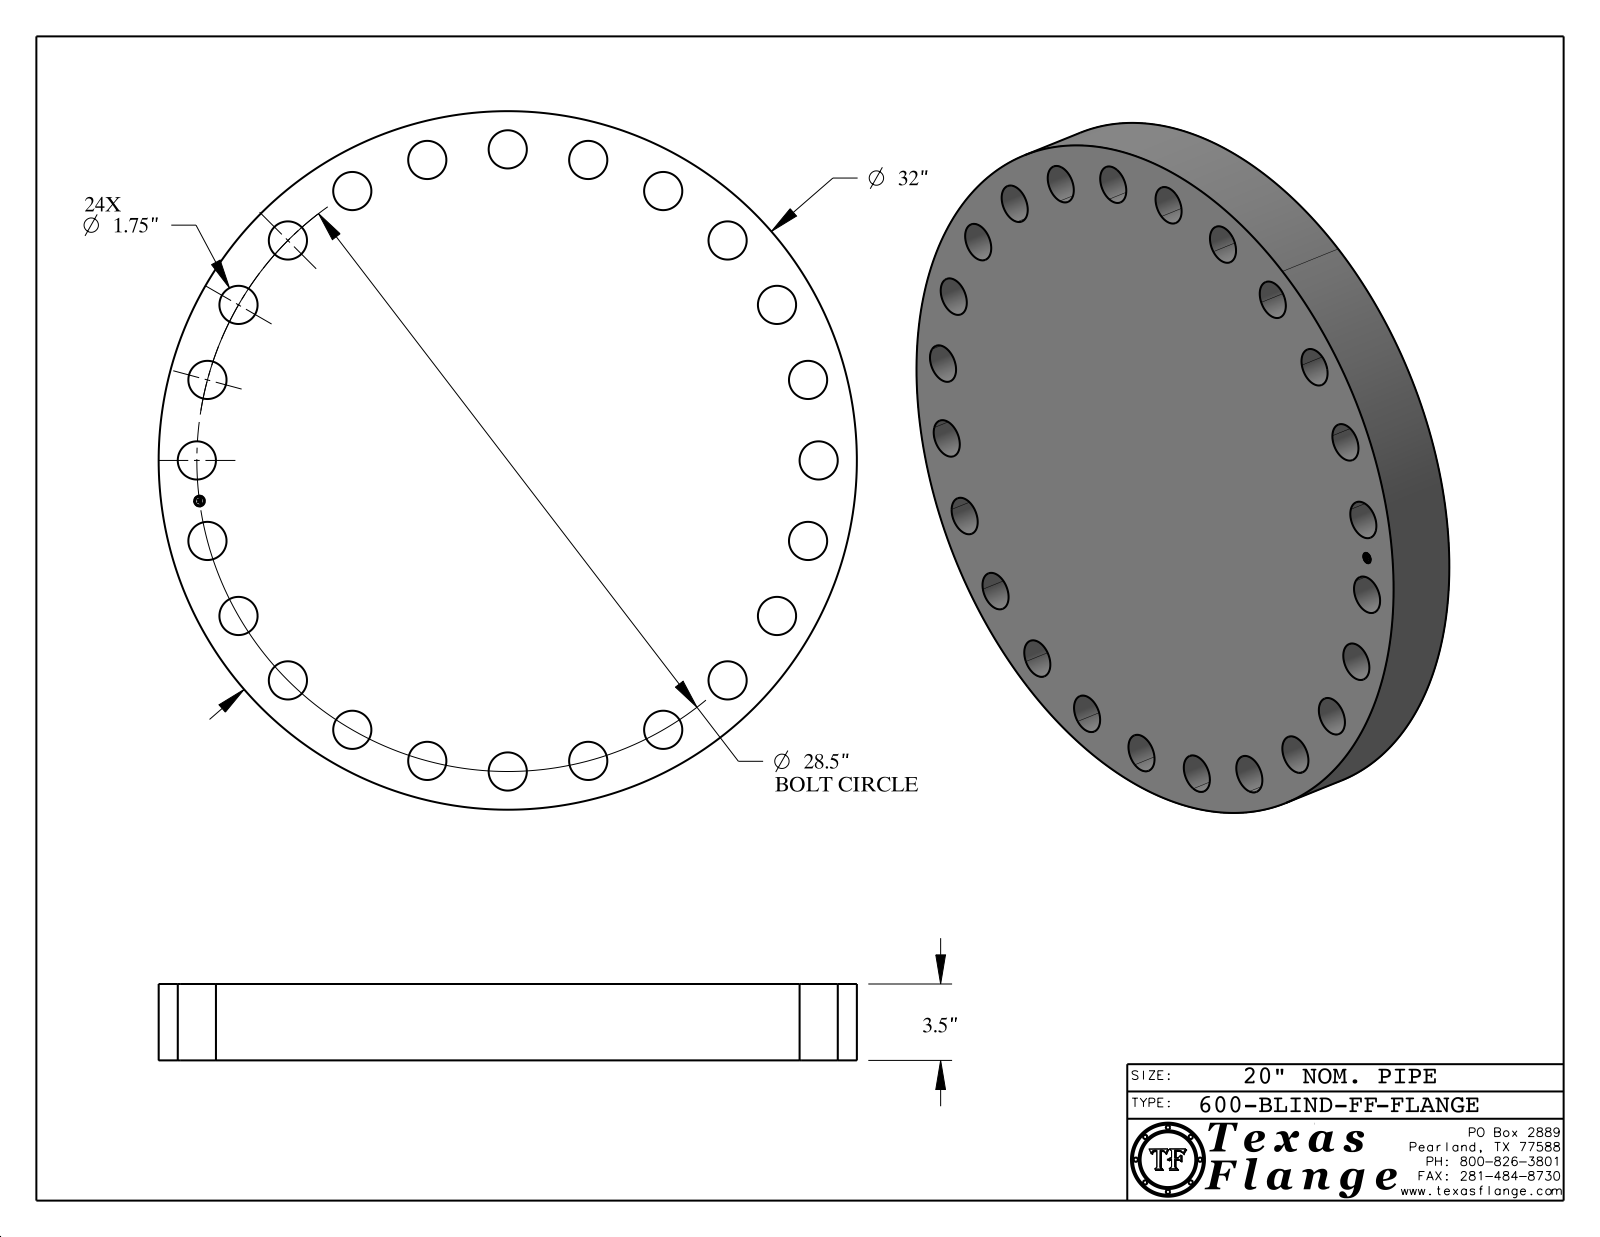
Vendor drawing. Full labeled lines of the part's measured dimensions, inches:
Part name (STEP PRODUCT): 600-BLIND-FF
STEP written by: CATIA V5 STEP AP214 (AUTOMOTIVE_DESIGN)
Units: inches
Bodies: 1 solid, 437 faces (367 planar, 70 cylindrical, 0 other)
Overall size (bounding box): 32 × 32 × 3.5
Volume: 2 613 in³ · Surface area: 2 307 in²
Round holes (diameter × count): ⌀1.75 ×24, ⌀0.495 ×1
Round bosses / shafts (diameter × count): ⌀0.03 ×8, ⌀32 ×1, ⌀0.39 ×1
Main face-to-face distances: 3.5, 0.015, 3.485, 0.148, 0.145, 0.027, 0.096, 0.122, 0.022, 0.101
Hole centre spacings: 3.72, 7.376, 24.682, 26.331, 27.529, 14.25, 20.153, 10.907
